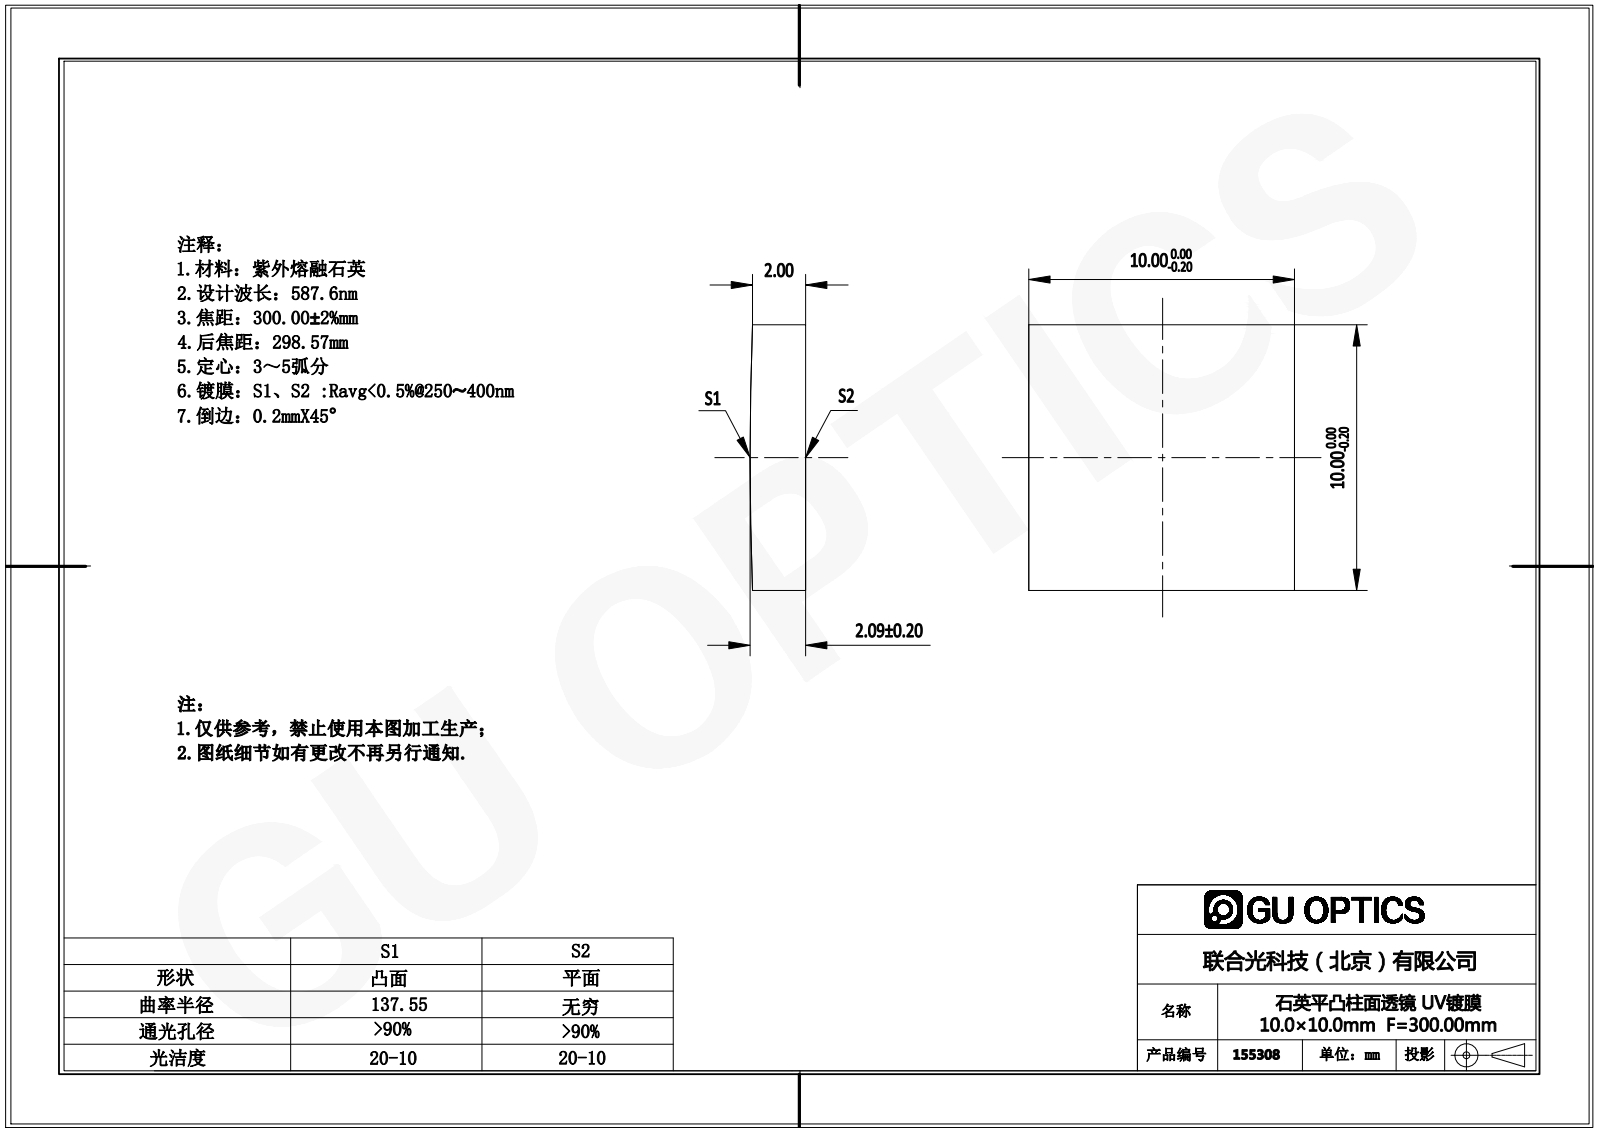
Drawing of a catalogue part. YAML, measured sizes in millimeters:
part_name: "155274"
step_written_by: "SolidWorks 2016 (AUTOMOTIVE_DESIGN)"
units: millimeters
bodies: {solids: 1, faces: 6, planar: 5, cylindrical: 1, other: 0}
overall_size: [10, 10, 2.09]
volume: 206
surface_area: 281
partial_cylinders:
  - {radius: 137.55, count: 1}
face_to_face_distances: [10]
